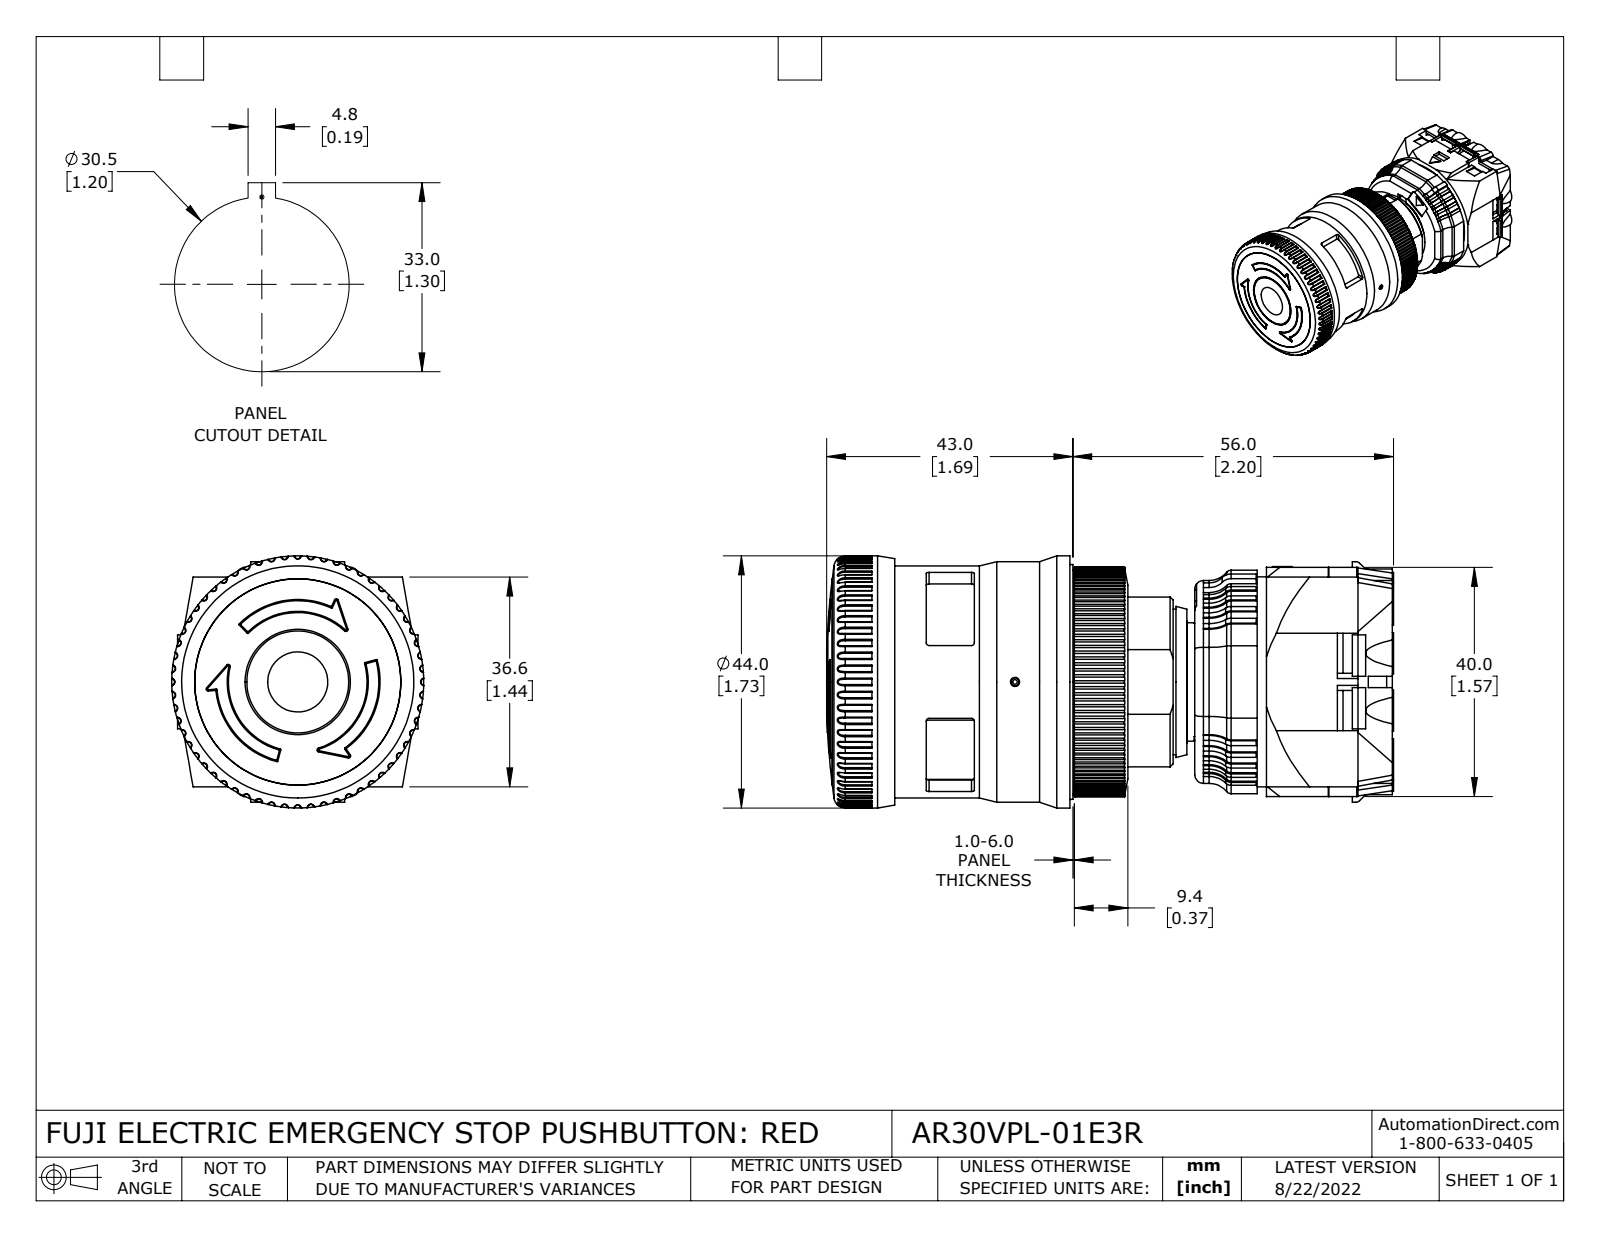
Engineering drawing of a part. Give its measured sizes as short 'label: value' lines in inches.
name: AR30VPL-01E3R
written by: SolidWorks 2021 (CONFIG_CONTROL_DESIGN)
unit: in
bodies: 32 solids, 2480 faces (1039 planar, 1119 cylindrical, 322 other)
size: 3.898 × 1.732 × 1.732
volume: 6.151 in³; area: 109.1 in²
holes: 12× ⌀0.138, 12× ⌀0.244, 2× ⌀0.13, 1× ⌀0.031, 1× ⌀0.063, 1× ⌀0.26, 1× ⌀0.315, 1× ⌀0.689, 1× ⌀0.693, 1× ⌀0.724, 1× ⌀0.827, 1× ⌀0.843
bosses: 12× ⌀0.283, 1× ⌀1.732, 1× ⌀1.654, 1× ⌀1.614, 1× ⌀1.535, 1× ⌀1.417, 1× ⌀1.299, 1× ⌀1.291
rounds: 120× R0.008, 120× R0.013, 76× R0.02, 24× R0.005, 19× R0.049, 19× R0.148, 15× R0.039, 12× R0.059
face distances: 0.118, 1.48, 0.039, 0.839, 1.598, 0.102, 1.516, 1.496, 1.378, 0.339
hole spacings: 0.641, 0.907, 0.325, 0.349, 0.394, 0.585, 0.713, 0.735
